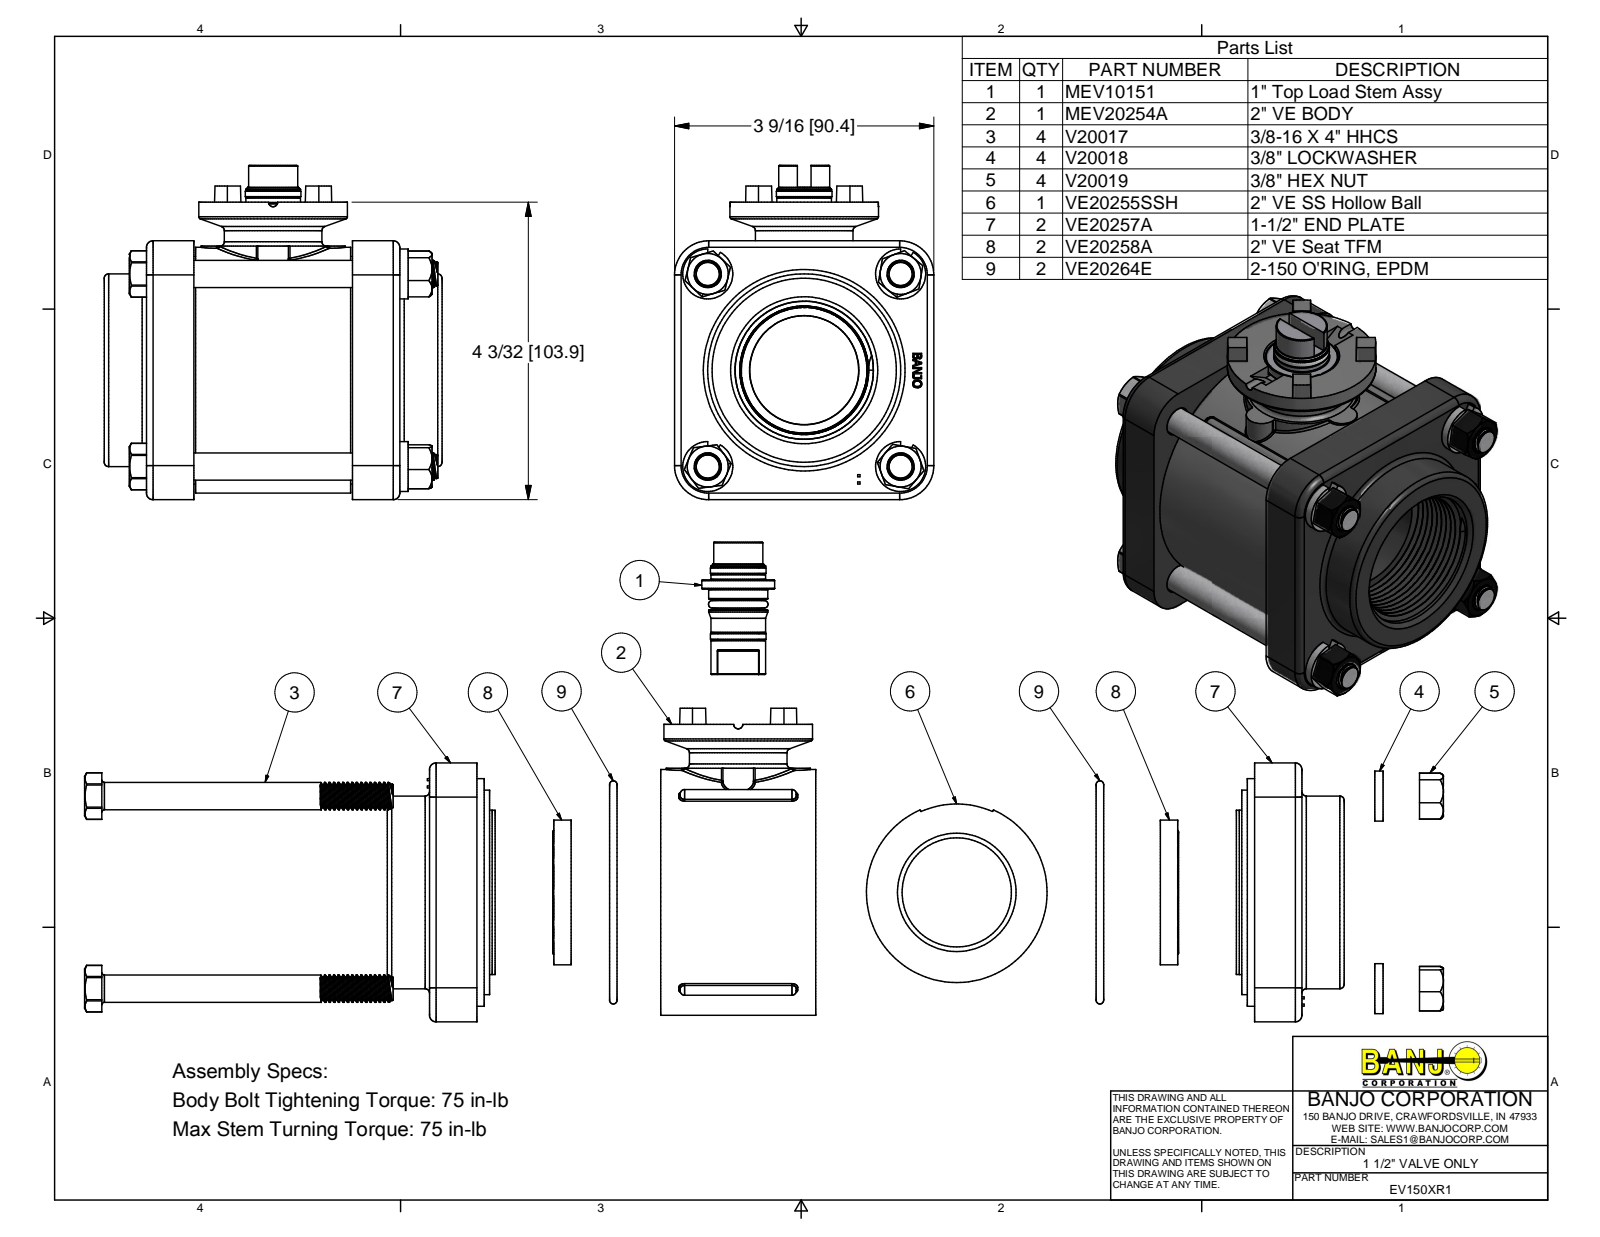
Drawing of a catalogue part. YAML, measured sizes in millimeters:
part_name: "MEV20254AX; MEV20254A; VE20255SSH; MEV10151SS (+8 more)"
step_written_by: "Autodesk Inventor 2014 (AUTOMOTIVE_DESIGN)"
units: millimeters
bodies: {solids: 26, faces: 1233, planar: 340, cylindrical: 359, other: 534}
overall_size: [117.81, 116.74, 90.42]
volume: 501678
surface_area: 163662
round_holes:
  - {diameter: 7.81, count: 4}
  - {diameter: 9.78, count: 4}
  - {diameter: 10.31, count: 4}
  - {diameter: 38.1, count: 2}
  - {diameter: 16.38, count: 1}
  - {diameter: 19.3, count: 1}
  - {diameter: 20.78, count: 1}
  - {diameter: 25.91, count: 1}
  - {diameter: 26.42, count: 1}
  - {diameter: 37.97, count: 1}
  - {diameter: 50.67, count: 1}
  - {diameter: 65.02, count: 1}
round_bosses_or_shafts:
  - {diameter: 8.24, count: 60}
  - {diameter: 17.46, count: 4}
  - {diameter: 9.52, count: 4}
  - {diameter: 85.85, count: 1}
  - {diameter: 79.5, count: 1}
  - {diameter: 71.42, count: 1}
  - {diameter: 67.31, count: 1}
  - {diameter: 57.4, count: 1}
partial_cylinders:
  - {radius: 2.29, count: 12}
  - {radius: 0.25, count: 8}
  - {radius: 0.51, count: 8}
  - {radius: 0.76, count: 8}
  - {radius: 4.12, count: 8}
  - {radius: 5.33, count: 4}
  - {radius: 8.12, count: 4}
  - {radius: 11.91, count: 4}
face_to_face_distances: [16.51, 71.83, 4.44, 20.95, 67.39, 50.88, 90.42, 48.34, 88.34, 55.32]
hole_center_spacings: [47.56, 67.26, 95.12]
